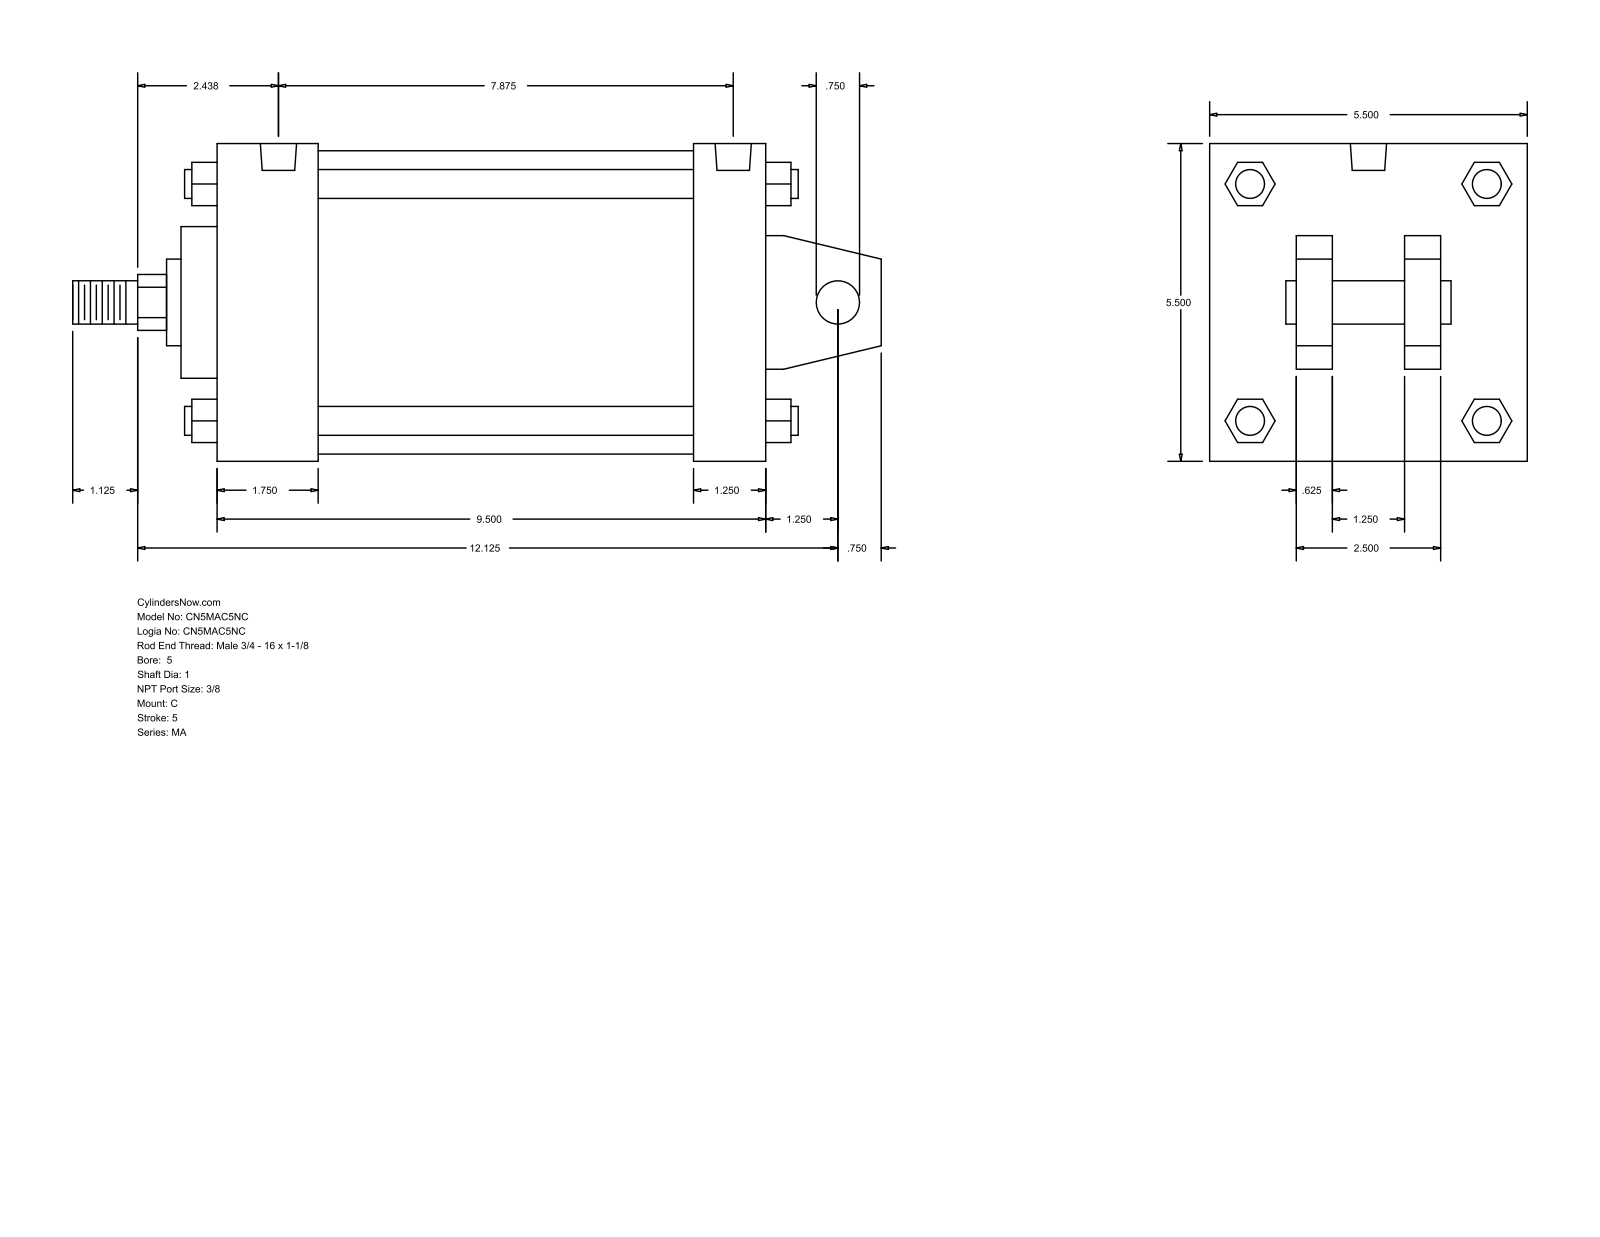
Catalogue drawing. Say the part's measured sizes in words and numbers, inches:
The part is named "MA_C__0500_1". Its 3-D file was written by "GSSL Pune (CONFIG_CONTROL_DESIGN)". It is 0 solids with 141 faces: 109 planar, 32 cylindrical and 0 other. Overall it measures 14 by 5.5 by 5.5 inches. Round holes: 4 of diameter 0.437, 2 of diameter 0.627. Round bosses or shafts: 4 of diameter 0.5, 2 of diameter 0.75, 1 of diameter 5.25, 1 of diameter 2.625, 1 of diameter 1.5, 1 of diameter 1. Partial cylindrical surfaces (rounded edges, fillets, slot ends): 1 of radius 0.484. The main face-to-face distances are 5.5, 9.5, 1.25, 0.625, 8.25, 1.75, 6.5, 7.75, 1.5, 4. The hole center spacings are 0.187, 7.5, 7.688, 7.875.
